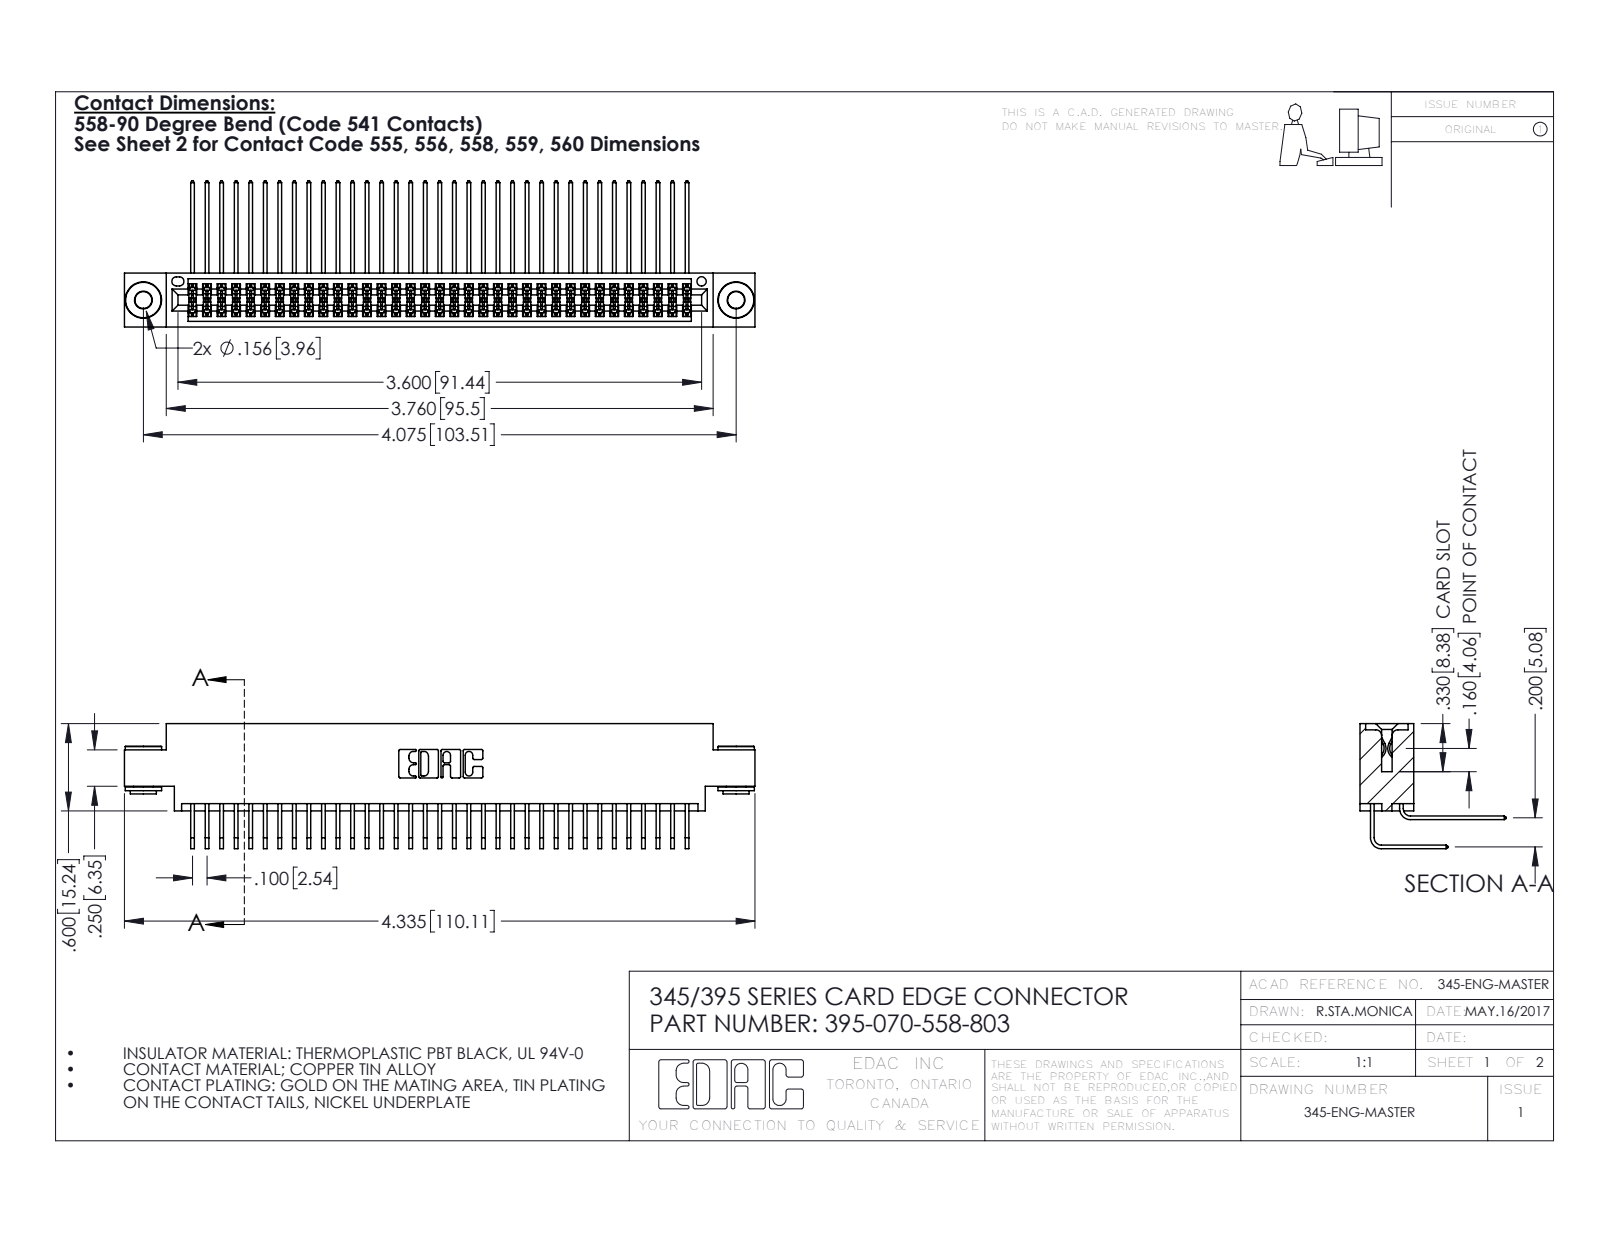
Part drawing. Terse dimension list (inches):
name: 345-292-001_558 Tail - 2; 345-292-001_558 559 Tail - 1; 345 Part_0.170 Offset - 0.156 Dia-TH; 395-070-558-803 (+1 more)
written by: SolidWorks 2016 (CONFIG_CONTROL_DESIGN)
unit: in
bodies: 73 solids, 3808 faces (2544 planar, 1256 cylindrical, 8 other)
size: 4.335 × 1.005 × 0.859
volume: 0.668 in³; area: 28.34 in²
holes: 2× ⌀0.116, 2× ⌀0.156, 1× ⌀0.064
bosses: 2× ⌀0.25, 2× ⌀0.18, 2× ⌀0.136
rounds: 106× R0.006, 22× R0.01, 6× R0.007, 6× R0.031, 3× R0.026, 2× R0.014, 2× R0.019, 2× R0.022
face distances: 0.072, 0.298, 0.2, 0.37, 0.098, 0.272, 0.025, 0.225, 0.175, 0.025
hole spacings: 0.27, 3.839, 4.075
